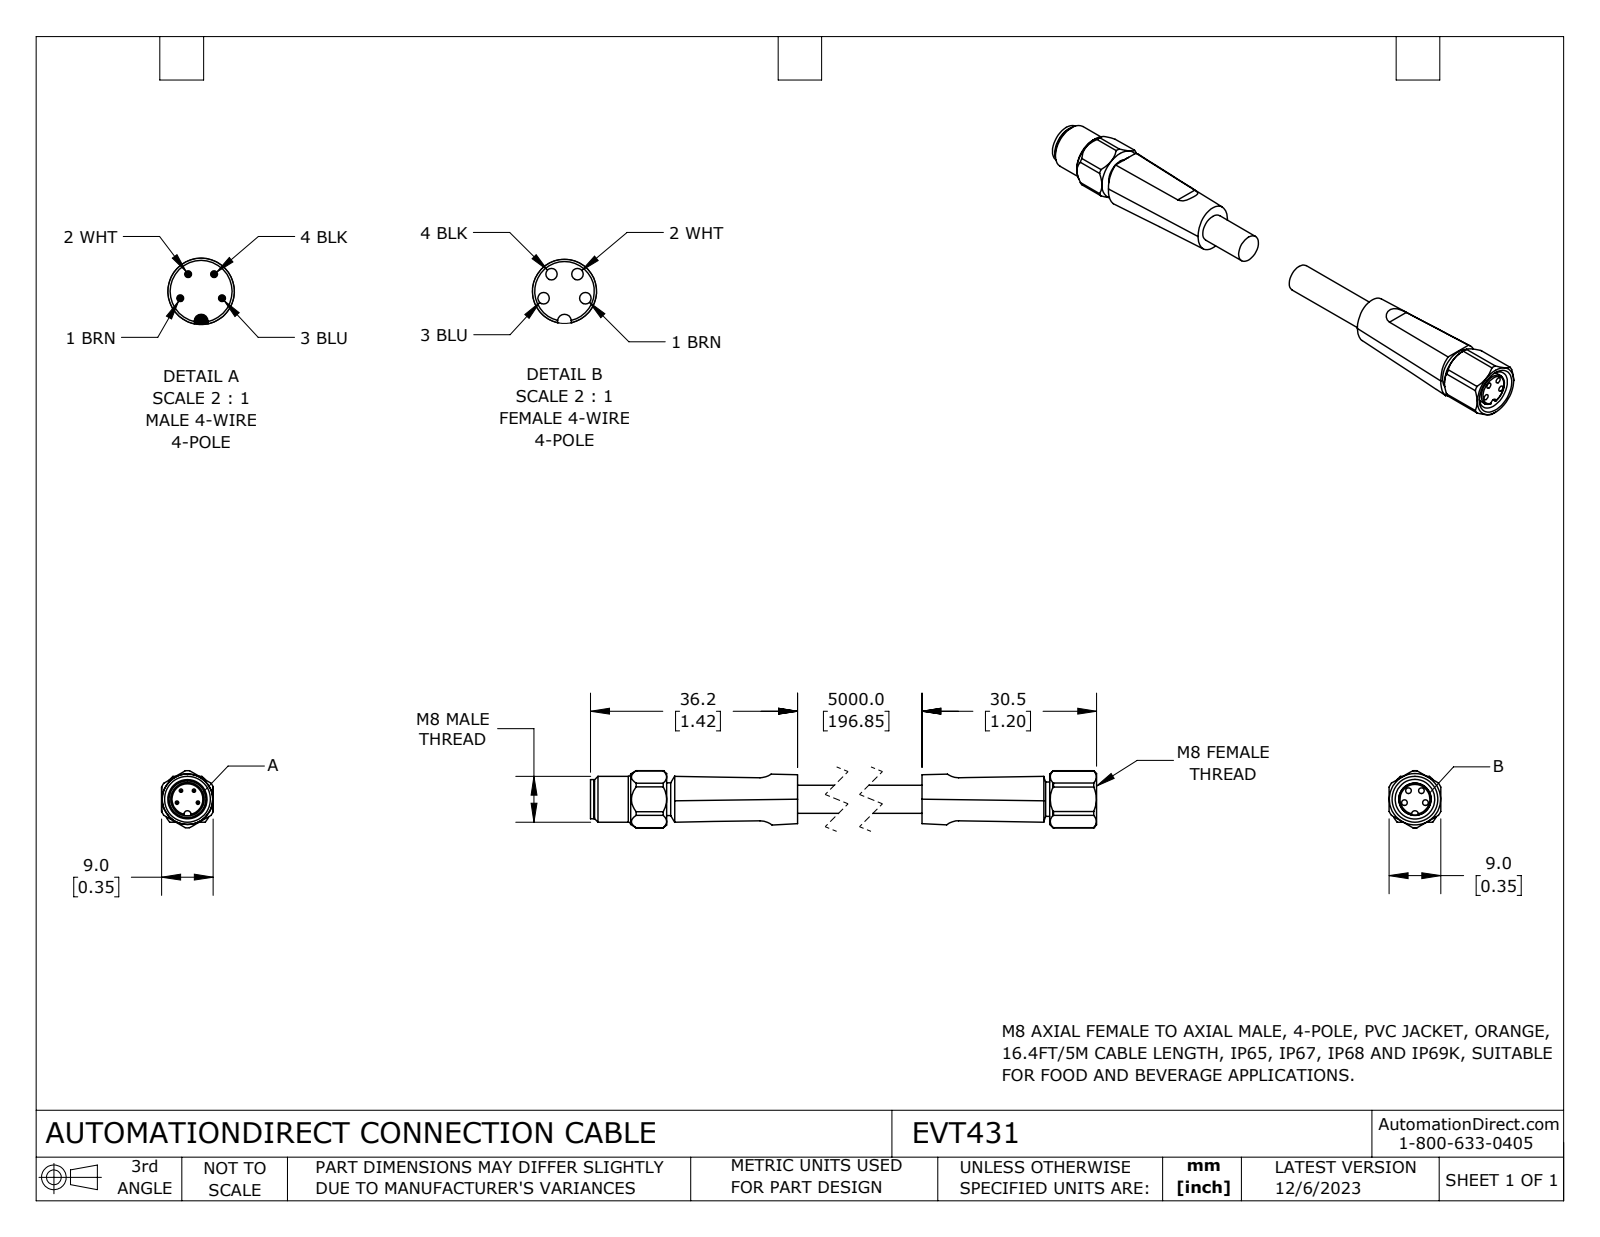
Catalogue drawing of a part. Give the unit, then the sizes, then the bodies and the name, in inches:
Units: inches
Overall size (bounding box): 4.173 × 0.393 × 0.354
Round holes (diameter × count): ⌀0.039 ×4, ⌀0.228 ×1, ⌀0.272 ×1
Round bosses / shafts (diameter × count): ⌀0.023 ×4, ⌀0.315 ×1, ⌀0.27 ×1, ⌀0.248 ×1, ⌀0.236 ×1, ⌀0.224 ×1, ⌀0.222 ×1, ⌀0.193 ×1
Partial cylindrical surfaces — rounded edges, fillets, slot ends (radius × count): R0.133 ×4, R0.024 ×1, R0.196 ×1, R0.196 ×1
Main face-to-face distances: 0.354, 0.26, 0.26, 0.354, 3.327, 1.201, 2.449, 0.878, 0.9, 1.549
Hole centre spacings: 0.074, 0.076, 0.087, 0.143, 0.089, 0.143
Volume: 0.244 in³ · Surface area: 4.751 in²
Bodies: 2 solids, 150 faces (47 planar, 58 cylindrical, 45 other)
Part name (STEP PRODUCT): EVT431; EVT431_MALE; EVT431_FEMALE
STEP written by: SolidWorks 2023 (CONFIG_CONTROL_DESIGN)
